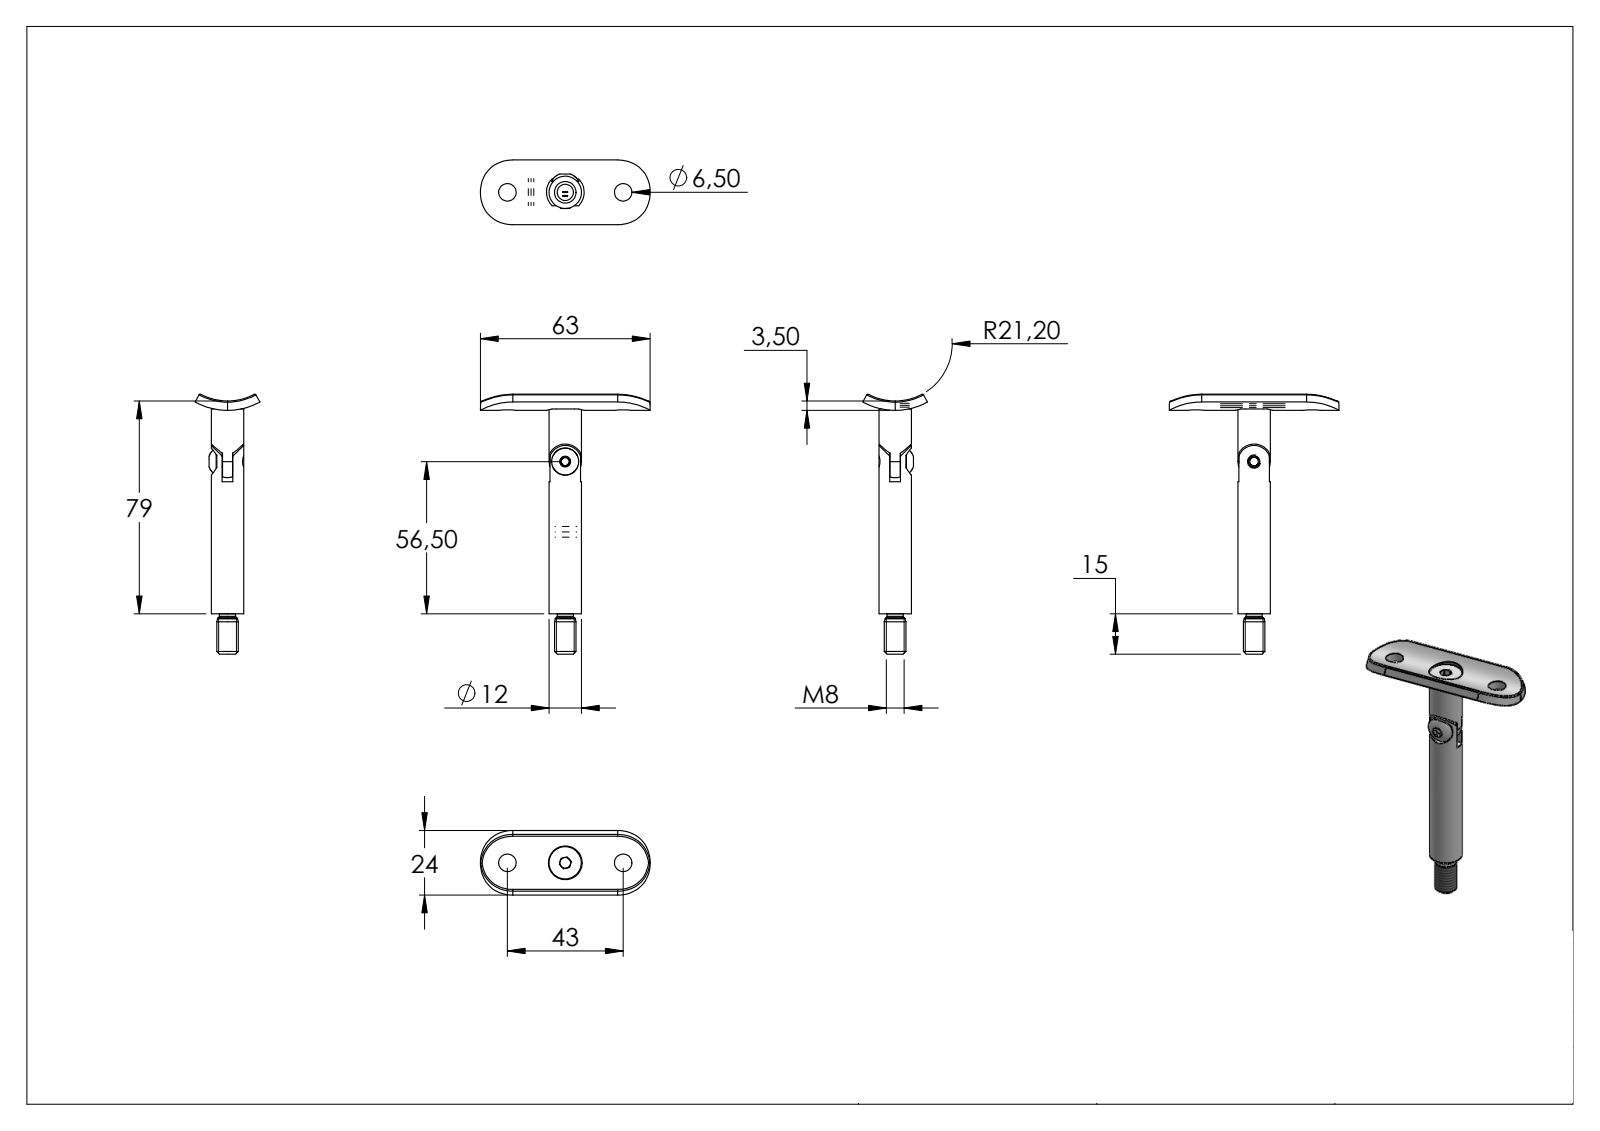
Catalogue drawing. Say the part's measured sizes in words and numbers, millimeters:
The part is named "50232-240-12 Teil2; 60182-240; DIN-7991_-_DIN7991 M6x16_DIN7991 M6x12; 50232-240-12 Teil1_50232-240-12 Teil1 (+8 more)". Its 3-D file was written by "SolidWorks 2018 (CONFIG_CONTROL_DESIGN)". It is 5 solids with 298 faces: 157 planar, 32 cylindrical and 109 other. Overall it measures 97.5 by 63 by 24 millimeters. Its volume is 13 302 cubic millimeters and its surface area 8 344 square millimeters. Round holes: 2 of diameter 6.5, 1 of diameter 4.2, 1 of diameter 5, 1 of diameter 5.5, 1 of diameter 8, 1 of diameter 12.5. Round bosses or shafts: 1 of diameter 12, 1 of diameter 9.5, 1 of diameter 6, 1 of diameter 4.02. Partial cylindrical surfaces (rounded edges, fillets, slot ends): 4 of radius 12, 2 of radius 0.5, 1 of radius 5, 1 of radius 6, 1 of radius 6.5, 1 of radius 7, 1 of radius 21.2, 1 of radius 24.7. The main face-to-face distances are 4, 6, 2, 2.8, 3.87, 2.13, 3.75, 3.88, 5.88, 27. The hole center spacings are 21, 42.
